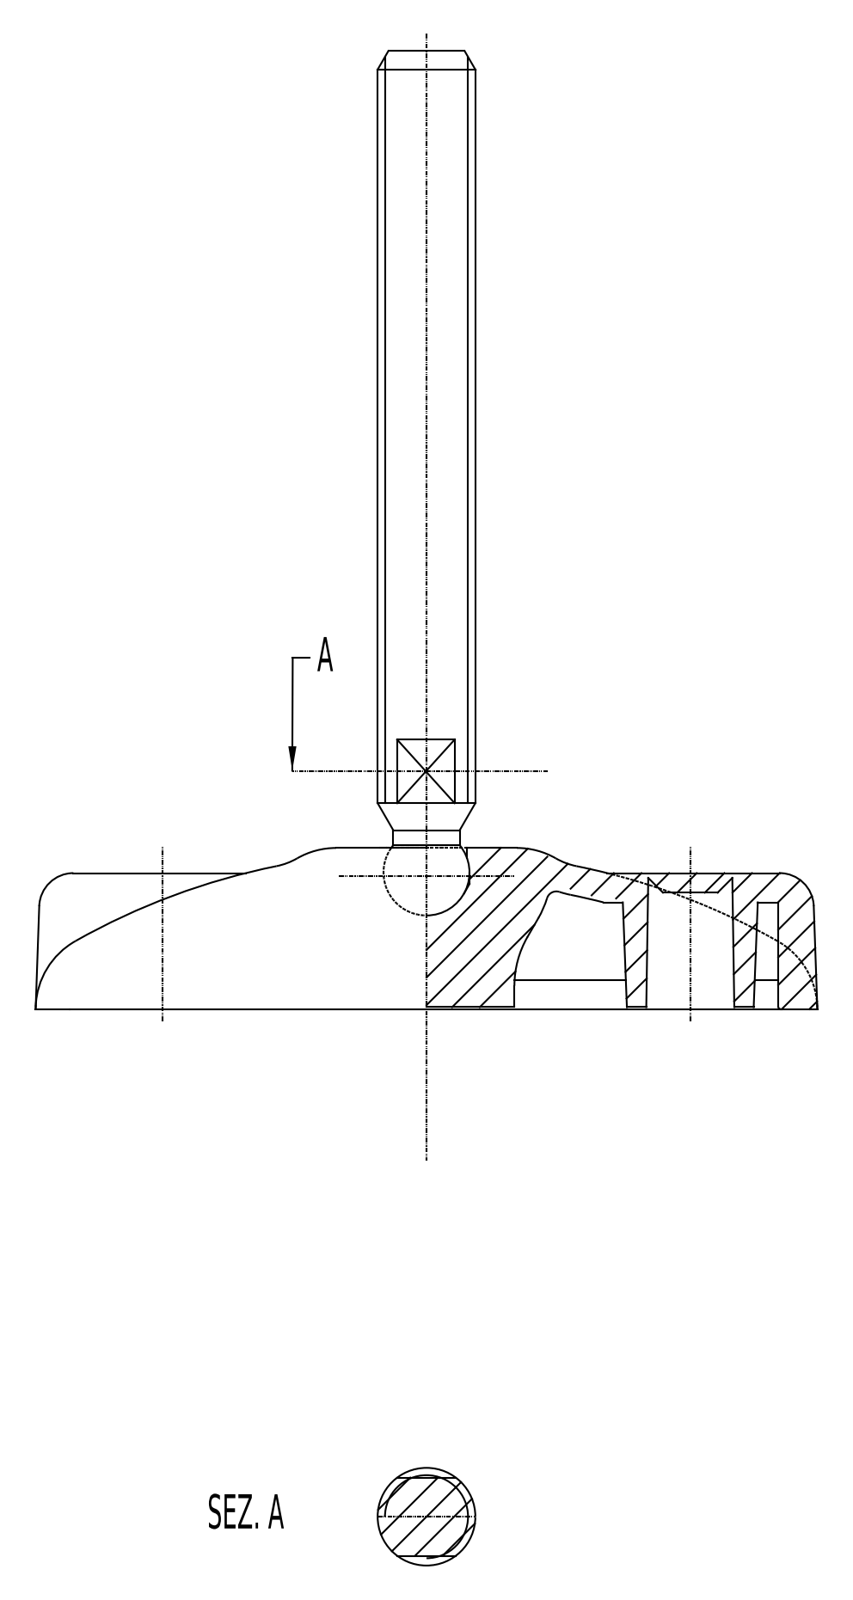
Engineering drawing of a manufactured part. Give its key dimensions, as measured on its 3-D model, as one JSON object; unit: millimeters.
{"step_written_by": "THINKDESIGN (CONFIG_CONTROL_DESIGN)", "units": "millimeters", "bodies": {"solids": 2, "faces": 58, "planar": 15, "cylindrical": 5, "other": 38}, "overall_size": [142.19, 80.01, 80.01], "volume_mm3": 52948, "surface_area_mm2": 17518, "round_holes": [[10.1, 1], [72.01, 1]], "round_bosses_or_shafts": [[18, 1], [10, 1], [6.8, 1]], "face_to_face_distances": [3, 14.33, 11.33, 16.5, 13.5, 2.17, 12.33, 9.33, 2, 4.17]}
